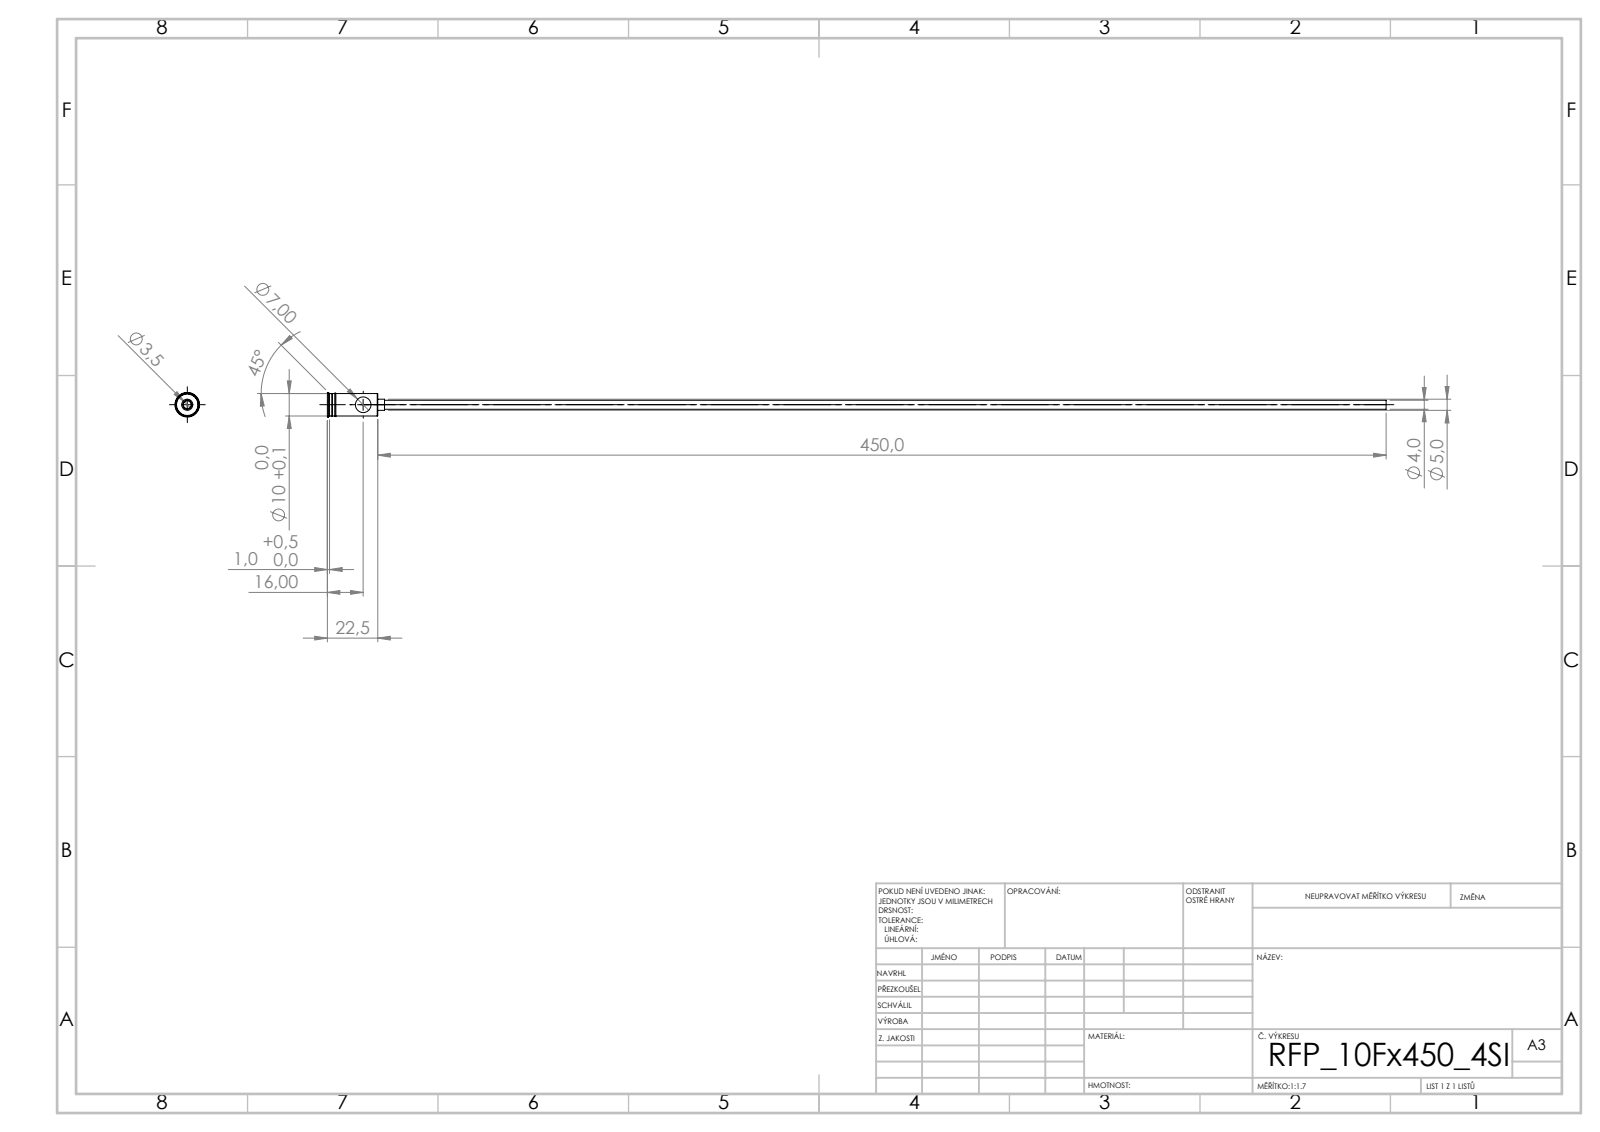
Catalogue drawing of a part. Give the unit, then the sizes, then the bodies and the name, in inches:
Units: inches
Overall size (bounding box): 18.602 × 0.433 × 0.433
Round holes (diameter × count): ⌀0.138 ×1, ⌀0.276 ×1
Round bosses / shafts (diameter × count): ⌀0.433 ×1, ⌀0.394 ×1, ⌀0.197 ×1, ⌀0.157 ×1
Main face-to-face distances: 0.886, 0.807, 0.079, 0.213, 0.795, 0.091, 0.118, 0.913, 0.925, 1.004
Volume: 0.164 in³ · Surface area: 18.11 in²
Bodies: 1 solid, 44 faces (20 planar, 16 cylindrical, 8 other)
STEP written by: SolidWorks 2019 (CONFIG_CONTROL_DESIGN)
